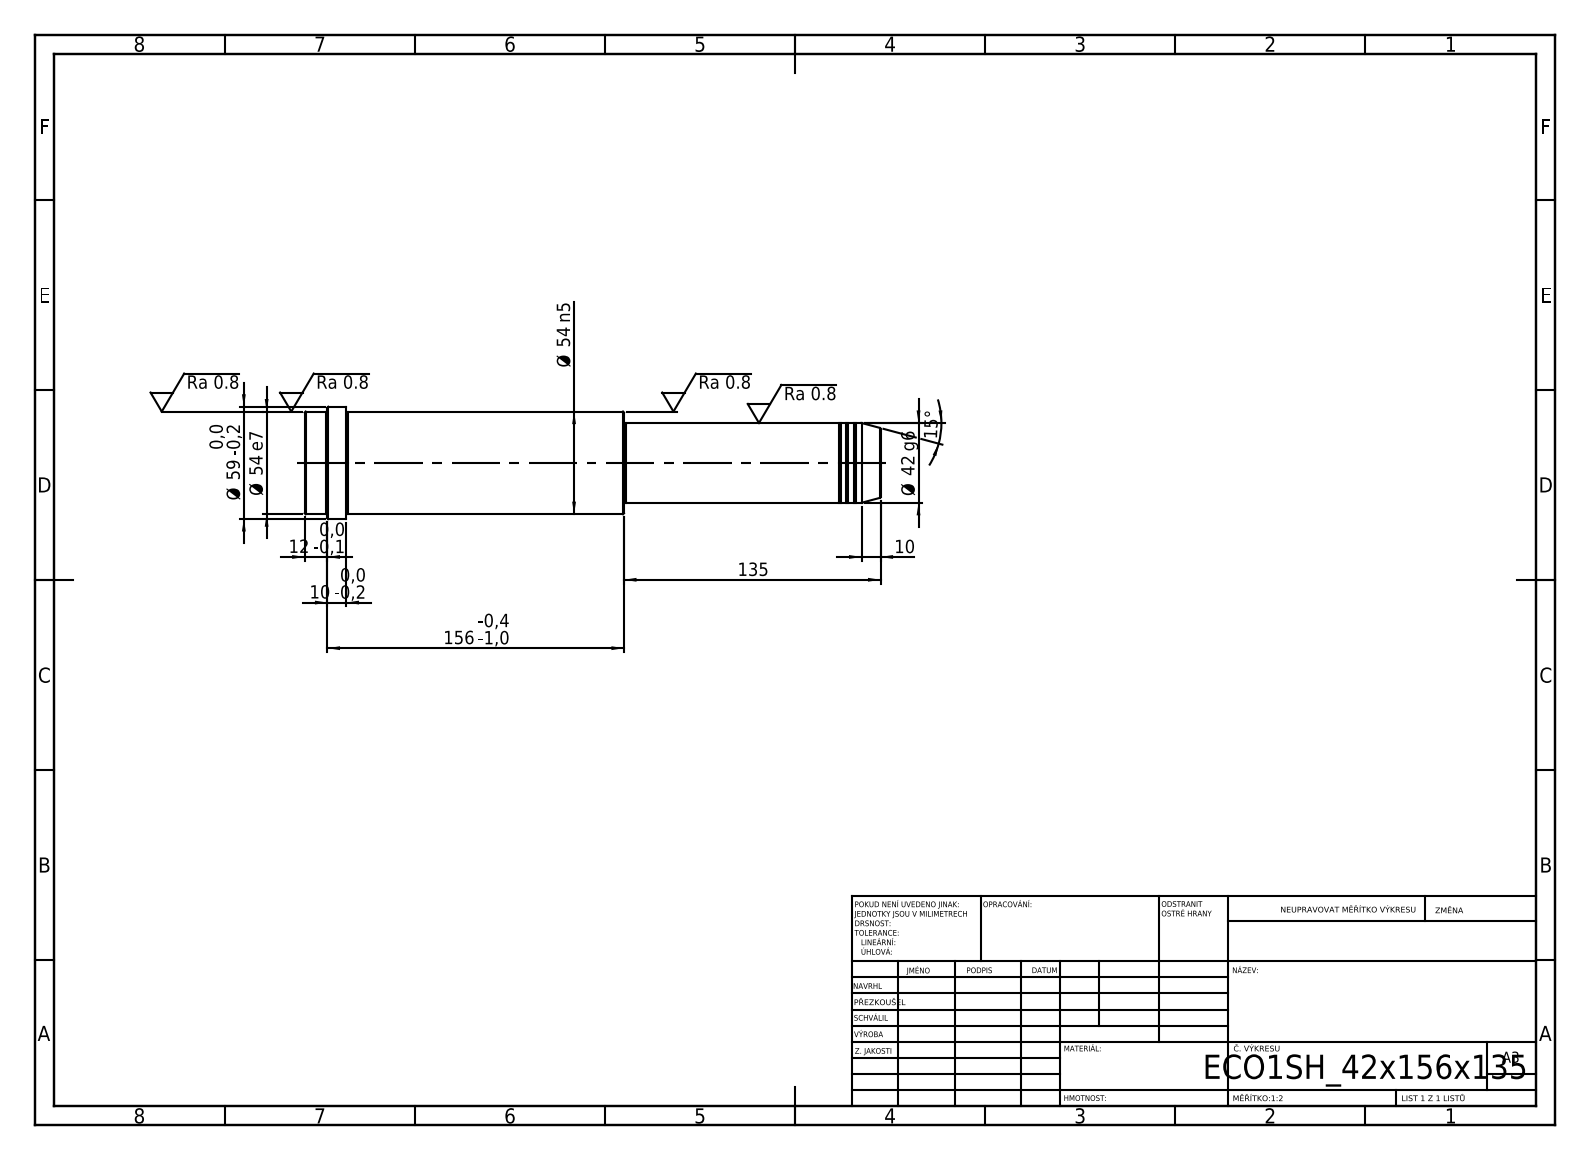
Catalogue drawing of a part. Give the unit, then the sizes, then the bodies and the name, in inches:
Units: inches
Overall size (bounding box): 11.929 × 2.323 × 2.323
Round bosses / shafts (diameter × count): ⌀2.323 ×1, ⌀2.126 ×1, ⌀1.654 ×1, ⌀1.614 ×1
Main face-to-face distances: 11.929, 5.315, 6.614, 11.063, 5.748, 0.866, 11.457, 6.142, 0.394, 0.472
Volume: 35.03 in³ · Surface area: 80.49 in²
Bodies: 1 solid, 52 faces (6 planar, 16 cylindrical, 30 other)
STEP written by: SolidWorks 2019 (CONFIG_CONTROL_DESIGN)
